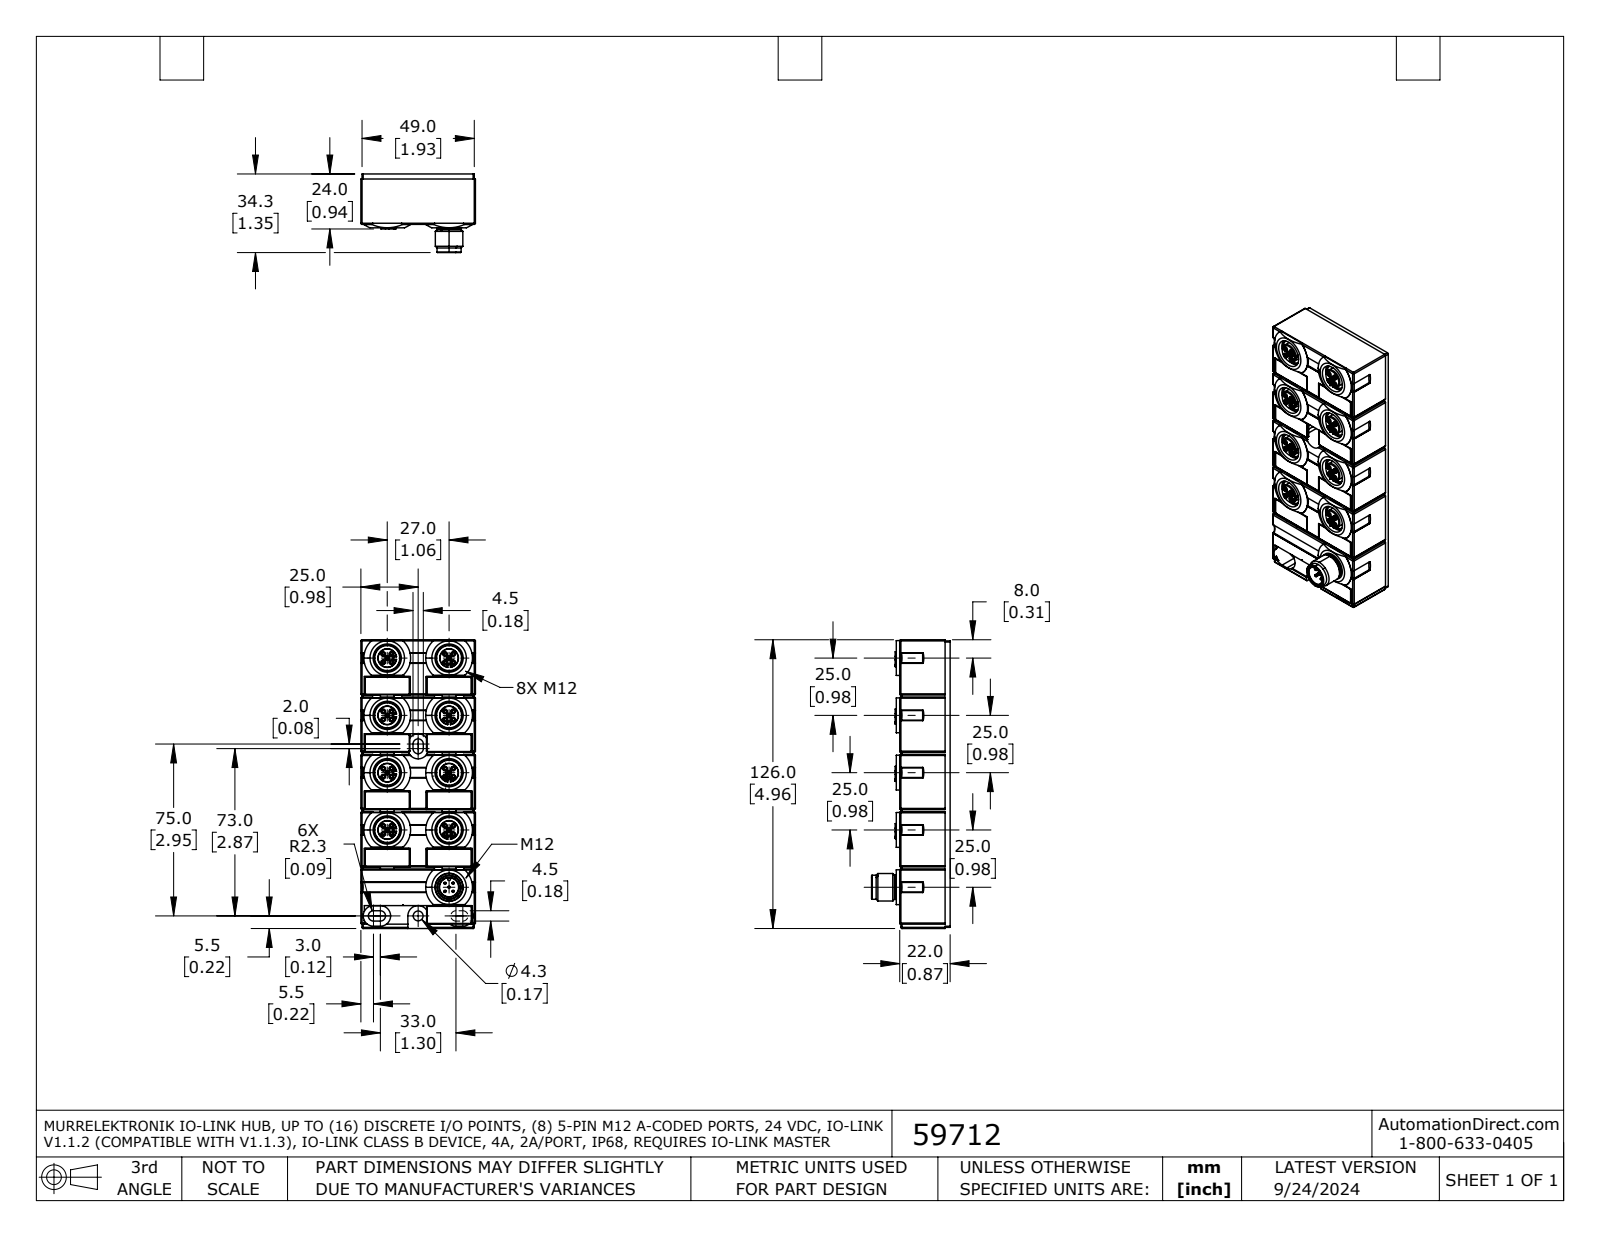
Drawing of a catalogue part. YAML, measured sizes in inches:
part_name: "59712"
step_written_by: "SolidWorks 2021 (AUTOMOTIVE_DESIGN)"
units: inches
bodies: {solids: 1, faces: 1315, planar: 476, cylindrical: 572, other: 267}
overall_size: [4.961, 1.969, 1.35]
volume: 8.157
surface_area: 45.15
round_holes:
  - {diameter: 0.047, count: 40}
  - {diameter: 0.484, count: 8}
  - {diameter: 0.43, count: 6}
  - {diameter: 0.43, count: 2}
  - {diameter: 0.169, count: 1}
  - {diameter: 0.327, count: 1}
round_bosses_or_shafts:
  - {diameter: 0.079, count: 40}
  - {diameter: 0.323, count: 8}
  - {diameter: 0.039, count: 5}
  - {diameter: 0.472, count: 1}
  - {diameter: 0.413, count: 1}
partial_cylinders:
  - {radius: 0.02, count: 77}
  - {radius: 0.01, count: 46}
  - {radius: 0.394, count: 15}
  - {radius: 0.402, count: 10}
  - {radius: 0.024, count: 8}
  - {radius: 0.045, count: 8}
  - {radius: 0.401, count: 8}
  - {radius: 0.089, count: 6}
face_to_face_distances: [1.969, 0.02, 0.864, 0.866, 0.059, 0.925, 0.061, 4.961, 1.949, 0.984]
hole_center_spacings: [0.098, 0.139, 1.063, 0.197, 0.996, 1.135, 1.072, 2.953]
